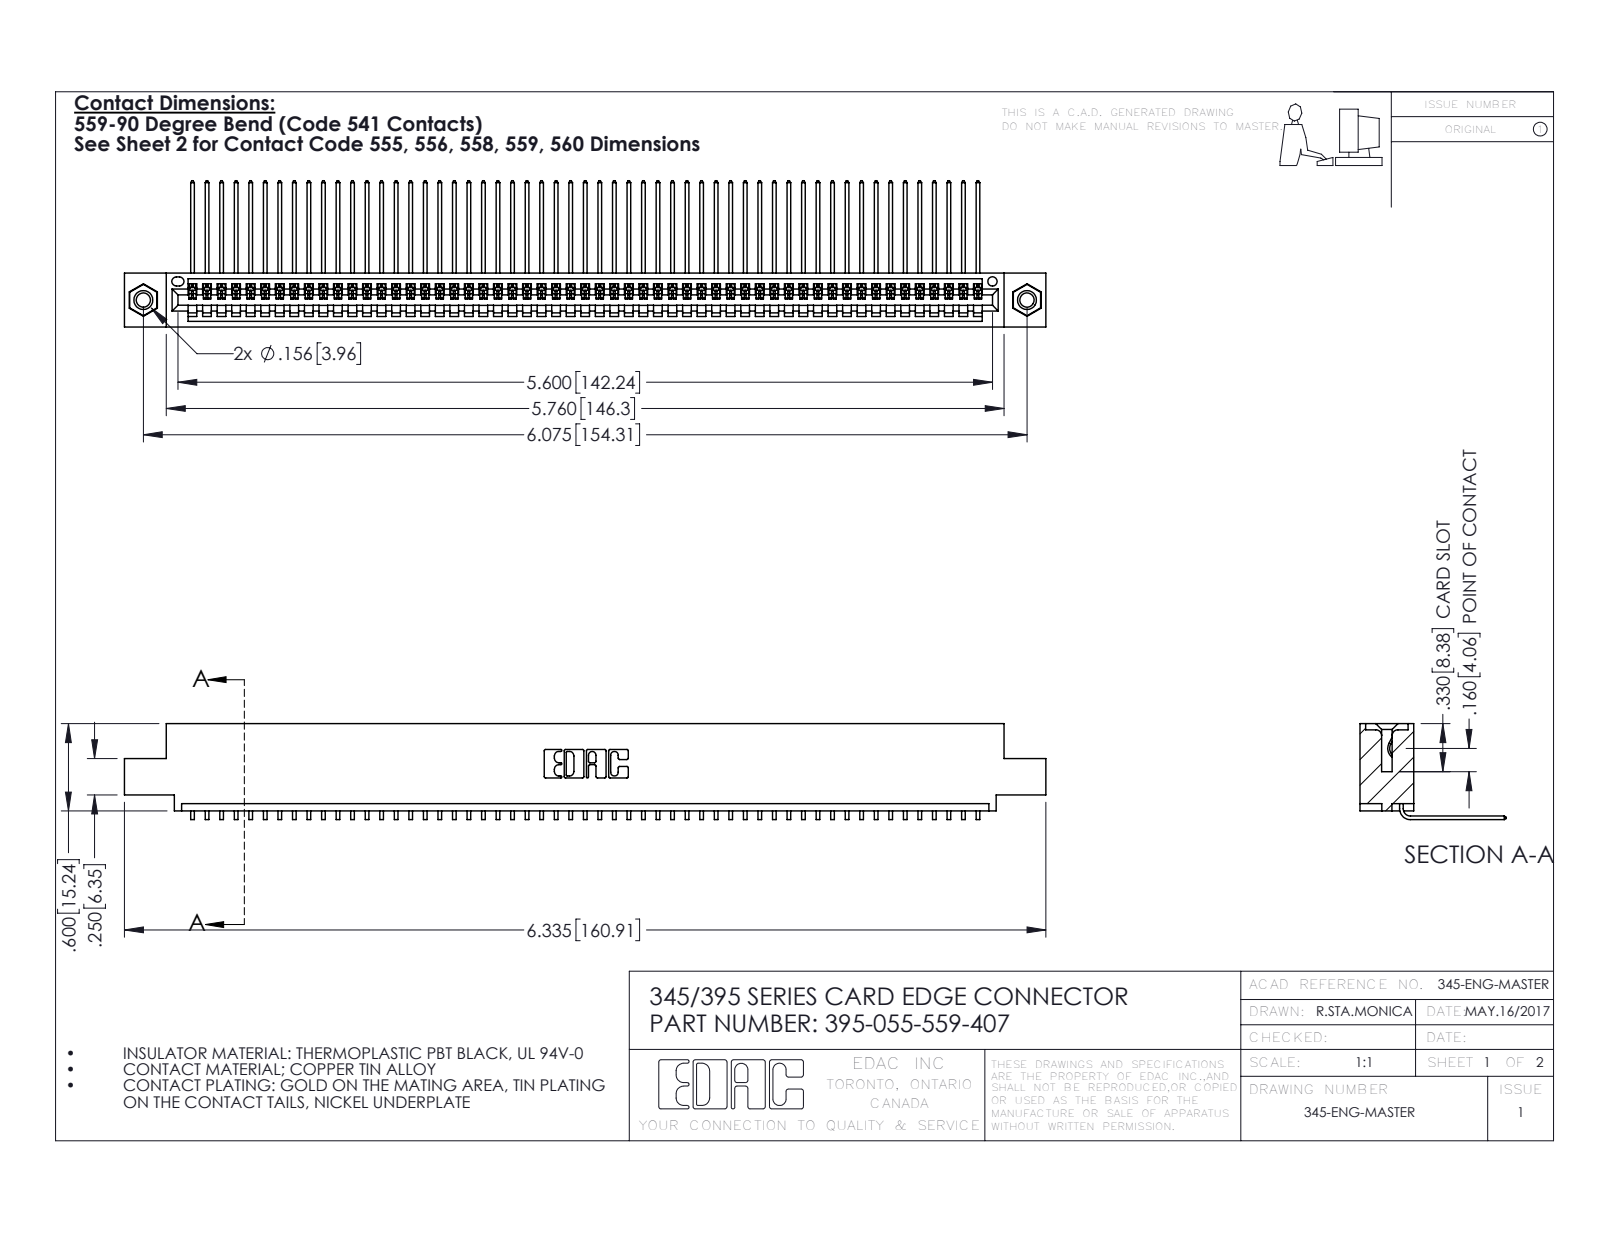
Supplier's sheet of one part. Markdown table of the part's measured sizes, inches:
| quantity | value |
| --- | --- |
| part name | 345-292-001_558 559 Tail - 1; 345-250-001_345-250-005-103; 345 Part_0.110 Offset - 0.156 Dia-TI; 395-055-559-407 |
| STEP written by | SolidWorks 2016 (CONFIG_CONTROL_DESIGN) |
| units | inches |
| bodies | 58 solids, 3490 faces (2426 planar, 1048 cylindrical, 16 other) |
| overall size | 6.335 × 1.005 × 0.659 |
| volume | 0.945 in³ |
| surface area | 34.02 in² |
| round holes (diameter × count) | 0.098 × 2, 0.125 × 2, 0.156 × 2, 0.064 × 1 |
| round bosses / shafts (diameter × count) | 0.155 × 2 |
| partial cylindrical surfaces (radius × count) | 0.006 × 110, 0.01 × 22, 0.007 × 6, 0.031 × 6, 0.026 × 3, 0.031 × 2, 0.04 × 2, 0.014 × 1 |
| main face-to-face distances | 0.072, 0.298, 0.37, 0.2, 0.098, 0.272, 0.025, 0.225, 0.149, 0.072 |
| hole center spacings | 0.27, 5.839, 6.075 |
